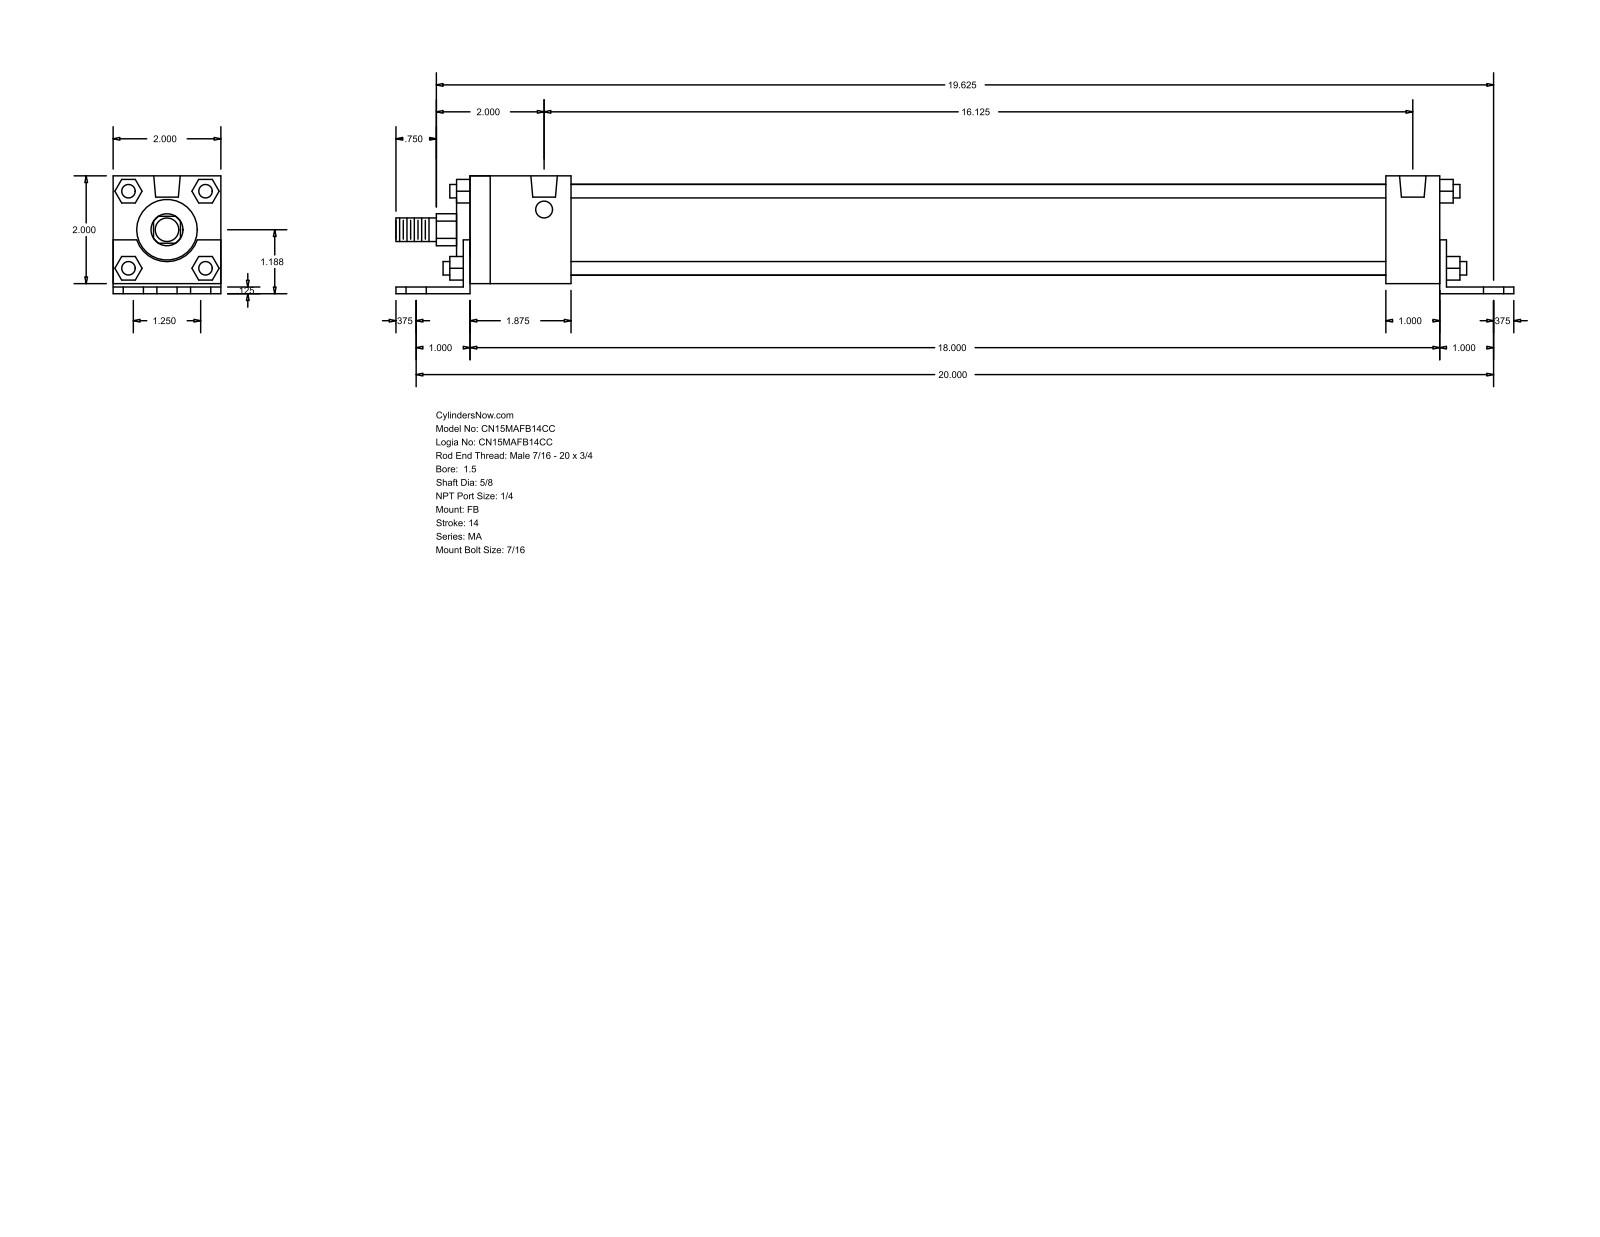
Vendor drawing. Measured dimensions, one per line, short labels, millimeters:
name: MA_FB__0150_0.625
written by: GSSL Pune (CONFIG_CONTROL_DESIGN)
unit: mm
bodies: 0 solids, 140 faces (105 planar, 35 cylindrical, 0 other)
size: 527.05 × 55.56 × 50.8
holes: 6× ⌀11.11, 4× ⌀7.94, 2× ⌀12.49
bosses: 4× ⌀6.35, 1× ⌀42.93, 1× ⌀28.57, 1× ⌀15.88, 1× ⌀11.11
rounds: 1× R7.54, 1× R15.05
face distances: 50.8, 3.17, 4.76, 55.56, 1.59, 52.39, 3.18, 460.37, 457.19, 6.35
hole spacings: 15.88, 508.26, 508.01, 31.76, 41.28, 62.38, 409.58, 447.96
